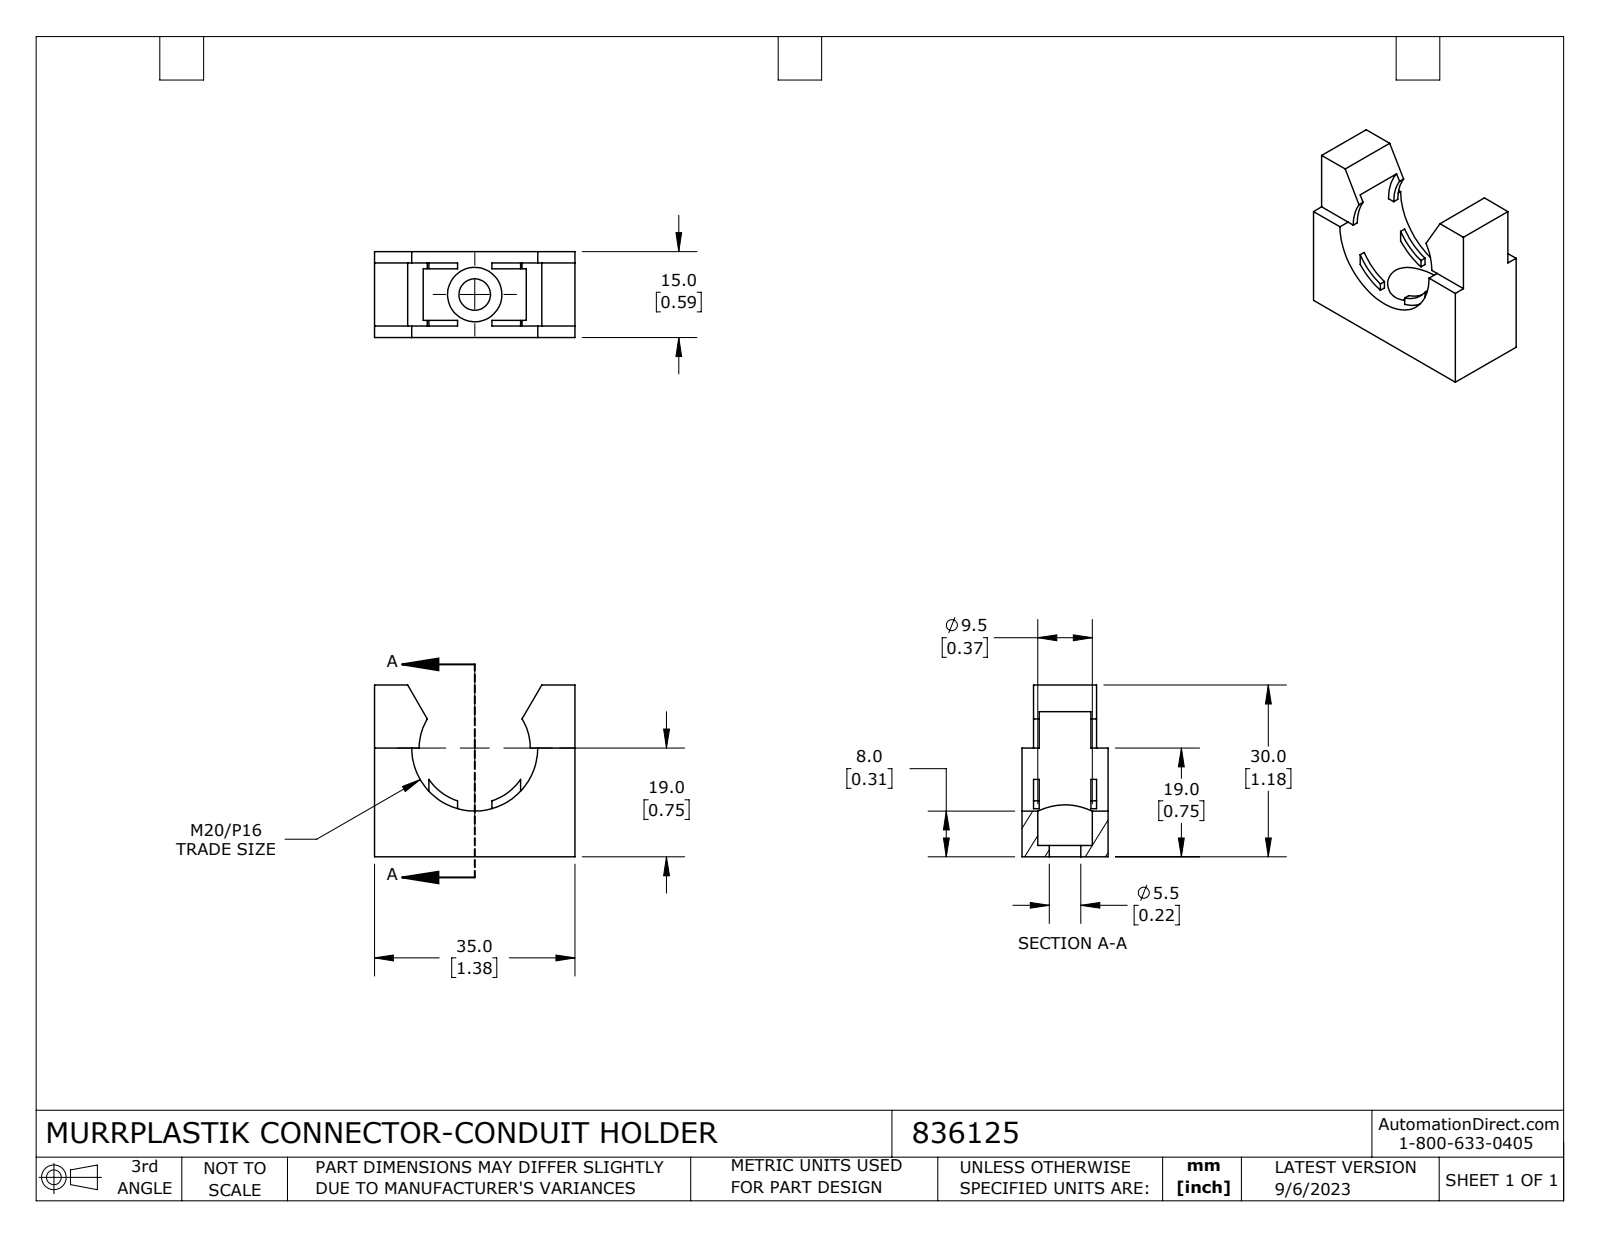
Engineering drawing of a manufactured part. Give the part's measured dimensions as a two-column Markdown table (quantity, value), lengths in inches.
| quantity | value |
| --- | --- |
| part name | 836125 |
| STEP written by | SolidWorks 2021 (CONFIG_CONTROL_DESIGN) |
| units | inches |
| bodies | 1 solid, 57 faces (42 planar, 15 cylindrical, 0 other) |
| overall size | 1.378 × 1.181 × 0.591 |
| volume | 0.514 in³ |
| surface area | 6.035 in² |
| round holes (diameter × count) | 0.217 × 1, 0.374 × 1 |
| partial cylindrical surfaces (radius × count) | 0.382 × 1, 0.433 × 1 |
| main face-to-face distances | 0.591, 0.079, 1.378, 0.512, 0.433, 1.181, 0.118, 0.472, 0.039, 0.394 |
